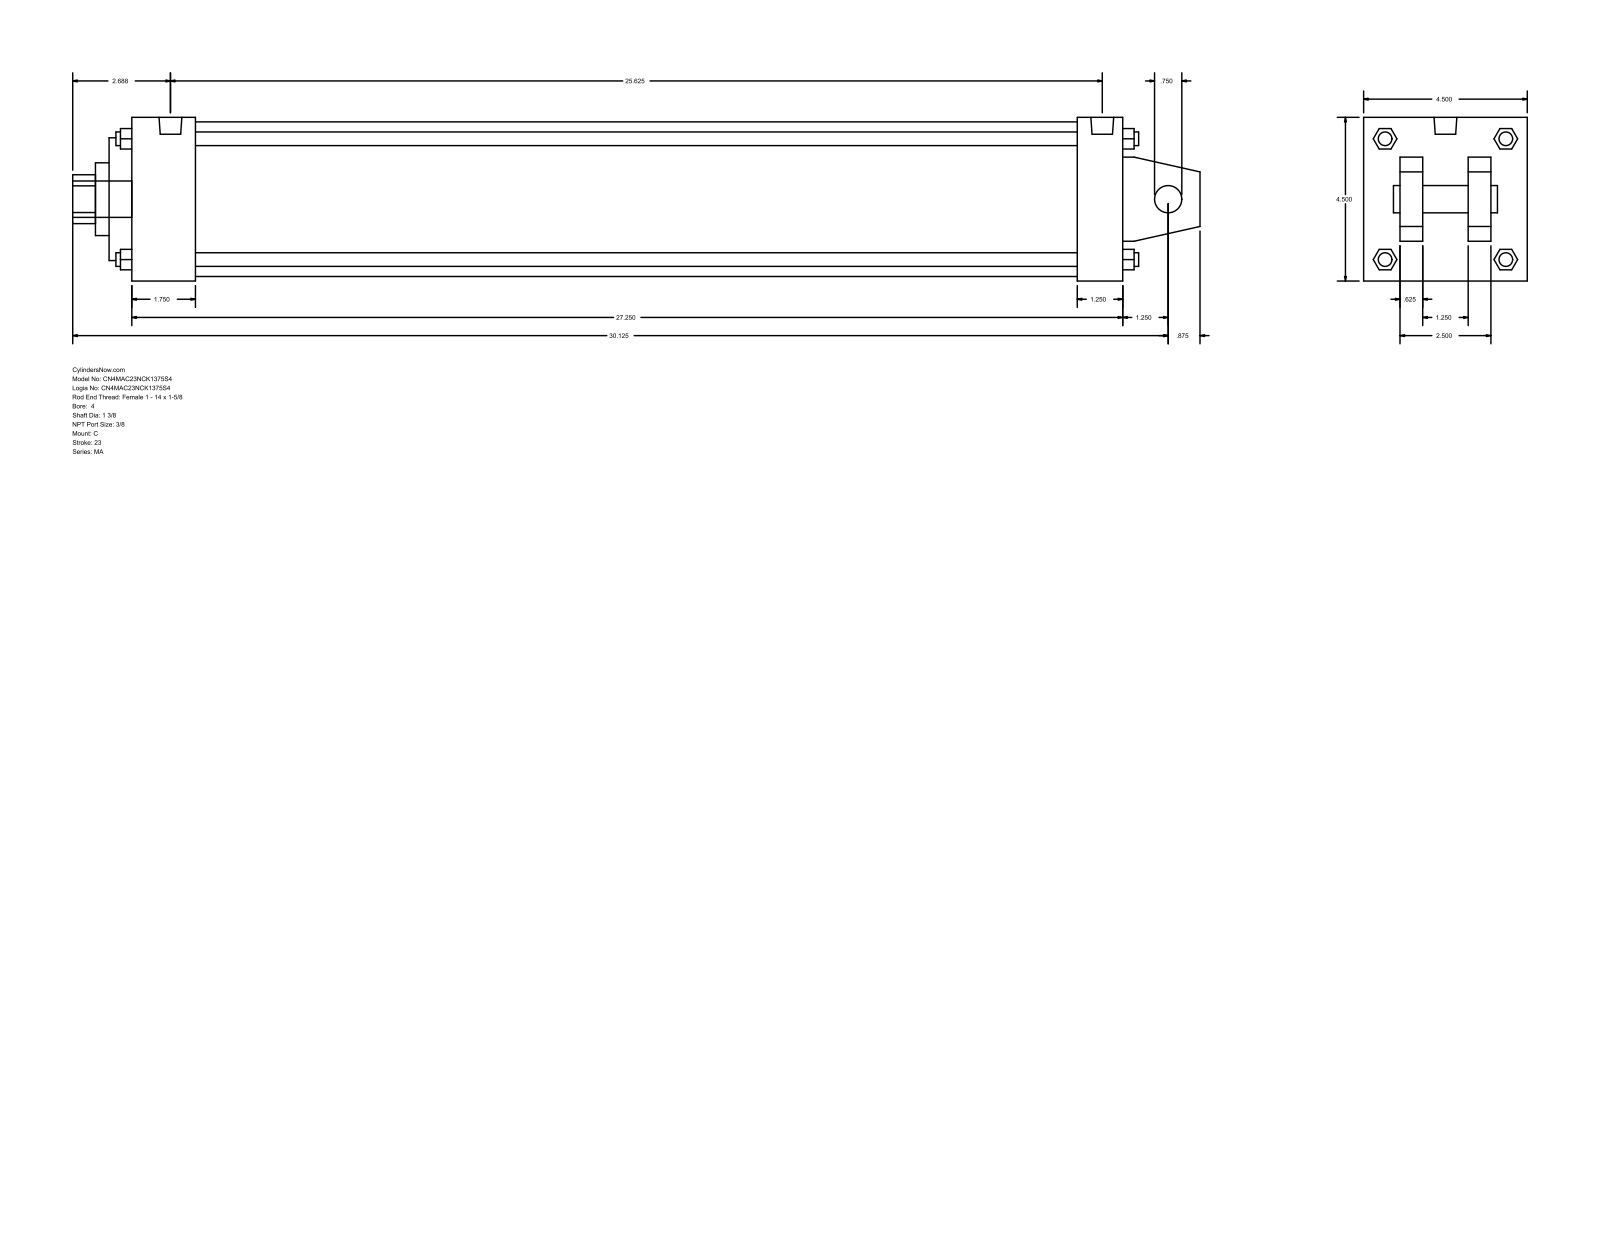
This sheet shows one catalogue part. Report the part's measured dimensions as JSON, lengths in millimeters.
{"part_name": "MA_C__0400_1.375", "step_written_by": "GSSL Pune (CONFIG_CONTROL_DESIGN)", "units": "millimeters", "bodies": {"solids": 0, "faces": 141, "planar": 109, "cylindrical": 32, "other": 0}, "overall_size": [787.4, 114.3, 114.3], "round_holes": [[19.05, 1], [34.92, 1], [50.8, 1], [85.72, 1], [107.95, 1]], "round_bosses_or_shafts": [[11.11, 4], [9.53, 4], [15.93, 2], [25.4, 1]], "partial_cylinders_radius": [[17.06, 1]], "face_to_face_distances": [114.3, 15.87, 692.15, 73.03, 41.27, 25.4, 88.9, 47.63, 708.02, 676.27]}
